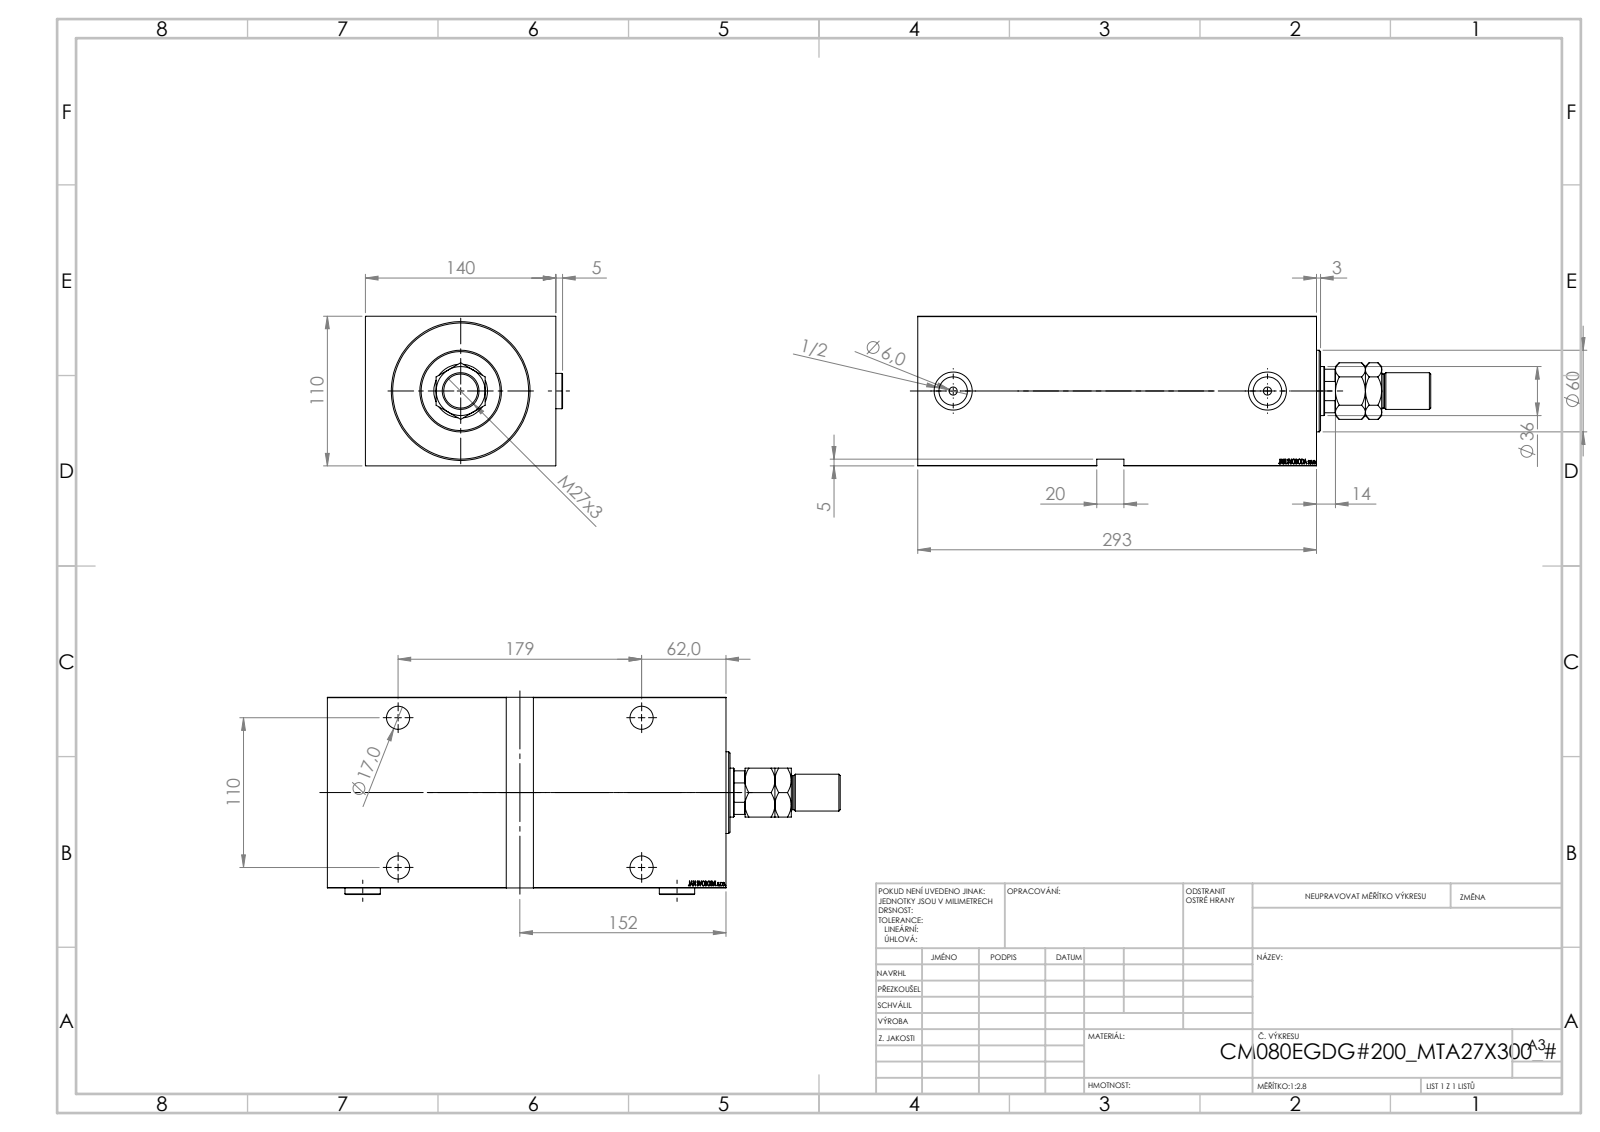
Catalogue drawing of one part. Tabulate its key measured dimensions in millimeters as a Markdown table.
| quantity | value |
| --- | --- |
| part name | MTA; V450CM_VC_B; V450CM_E_VCP; V450CM_E_Body (+1 more) |
| STEP written by | SolidWorks 2019 (CONFIG_CONTROL_DESIGN) |
| units | millimeters |
| bodies | 6 solids, 961 faces (461 planar, 72 cylindrical, 428 other) |
| overall size | 377 × 144.9 × 110 |
| volume | 3 626 000 mm³ |
| surface area | 361 922 mm² |
| round holes (diameter × count) | 17 × 4, 25 × 4, 6 × 2, 20.96 × 2, 28 × 2, 25.5 × 1, 36 × 1, 39.5 × 1, 80 × 1, 100 × 1 |
| round bosses / shafts (diameter × count) | 26 × 2, 82 × 1, 60 × 1, 27 × 1, 25 × 1 |
| partial cylindrical surfaces (radius × count) | 17.5 × 1 |
| main face-to-face distances | 110, 140, 293, 21, 272, 5, 288, 267, 79, 276.4 |
| hole center spacings | 110, 179, 210.1, 231 |
